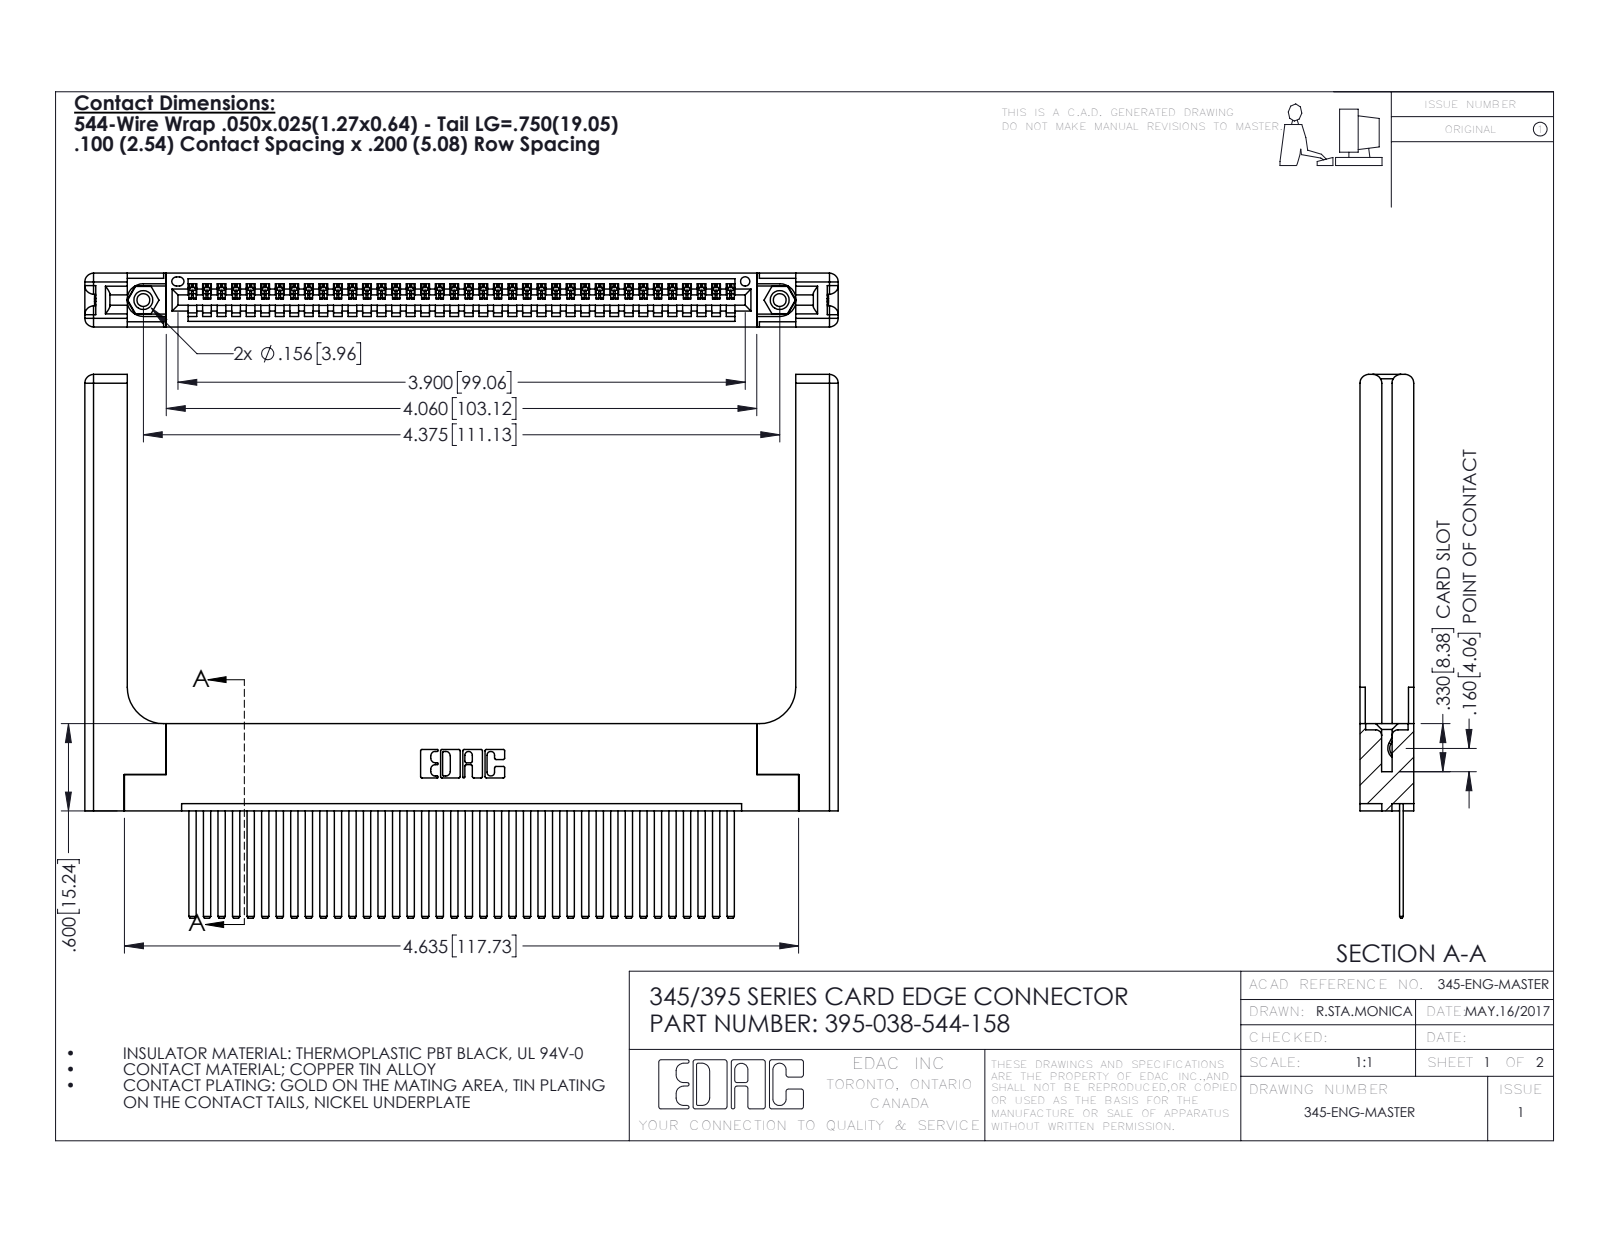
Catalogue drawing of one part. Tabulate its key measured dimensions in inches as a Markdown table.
| quantity | value |
| --- | --- |
| part name | 345-292-001_345-293-144; 345-250-001_345-250-001-102; 345 Part_Flush Mounting Lugs - 0.156 Dia-TH; 395-038-544-158 (+1 more) |
| STEP written by | SolidWorks 2016 (CONFIG_CONTROL_DESIGN) |
| units | inches |
| bodies | 43 solids, 2358 faces (1596 planar, 702 cylindrical, 60 other) |
| overall size | 5.179 × 3.737 × 0.37 |
| volume | 1.306 in³ |
| surface area | 36.76 in² |
| round holes (diameter × count) | 0.089 × 2, 0.125 × 2, 0.156 × 2, 0.064 × 1 |
| round bosses / shafts (diameter × count) | 0.155 × 2 |
| partial cylindrical surfaces (radius × count) | 0.006 × 76, 0.01 × 22, 0.06 × 16, 0.007 × 6, 0.031 × 6, 0.026 × 3, 0.03 × 2, 0.031 × 2 |
| main face-to-face distances | 0.072, 0.298, 0.37, 0.098, 0.272, 0.025, 0.2, 0.148, 0.15, 0.225 |
| hole center spacings | 0.27, 4.139, 4.375 |
